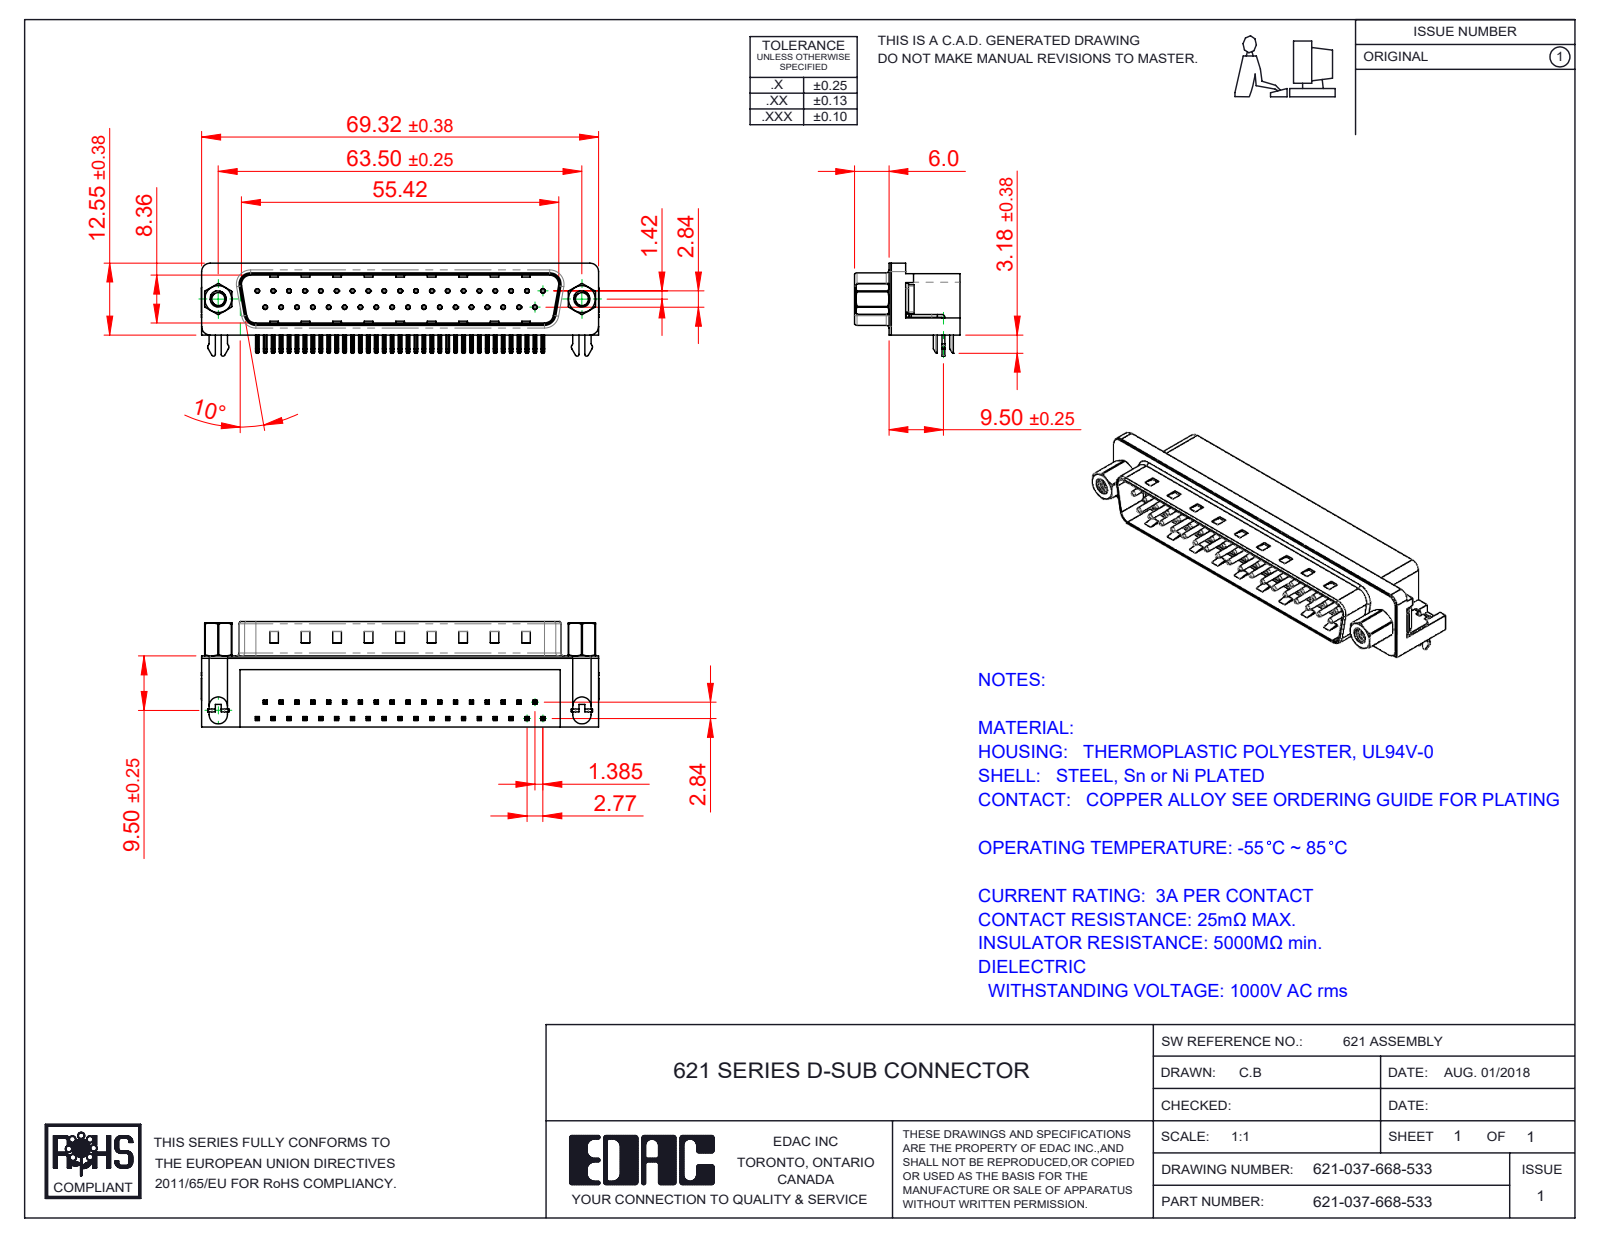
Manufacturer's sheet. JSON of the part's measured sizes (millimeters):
{"part_name": "621-037-668-533; 621 2 Prong Board Lock; 621 4-40 Threaded Rivet; 621 Housing_37 Socket (+4 more)", "step_written_by": "SolidWorks 2016 (CONFIG_CONTROL_DESIGN)", "units": "millimeters", "bodies": {"solids": 45, "faces": 3365, "planar": 2067, "cylindrical": 995, "other": 303}, "overall_size": [69.4, 18.4, 16.25], "volume_mm3": 8834, "surface_area_mm2": 10583, "round_holes": [[0.35, 37], [0.8, 37], [2.26, 2], [2.29, 2], [4, 2], [4.8, 2], [5, 2]], "round_bosses_or_shafts": [[0.75, 37], [4.9, 2], [4.75, 2], [3.9, 2], [2.79, 2]], "partial_cylinders_radius": [[0.25, 156], [0.12, 74], [1, 16], [0.5, 14], [1.6, 8], [1.5, 7], [0.32, 4], [0.9, 4]], "face_to_face_distances": [0.4, 12, 10.35, 8.76, 1.7, 2.1, 10.46, 10.86, 12.4, 9], "hole_center_spacings": [3.16, 2.77, 5.54, 8.31, 11.08, 13.85, 19.39, 22.16]}
